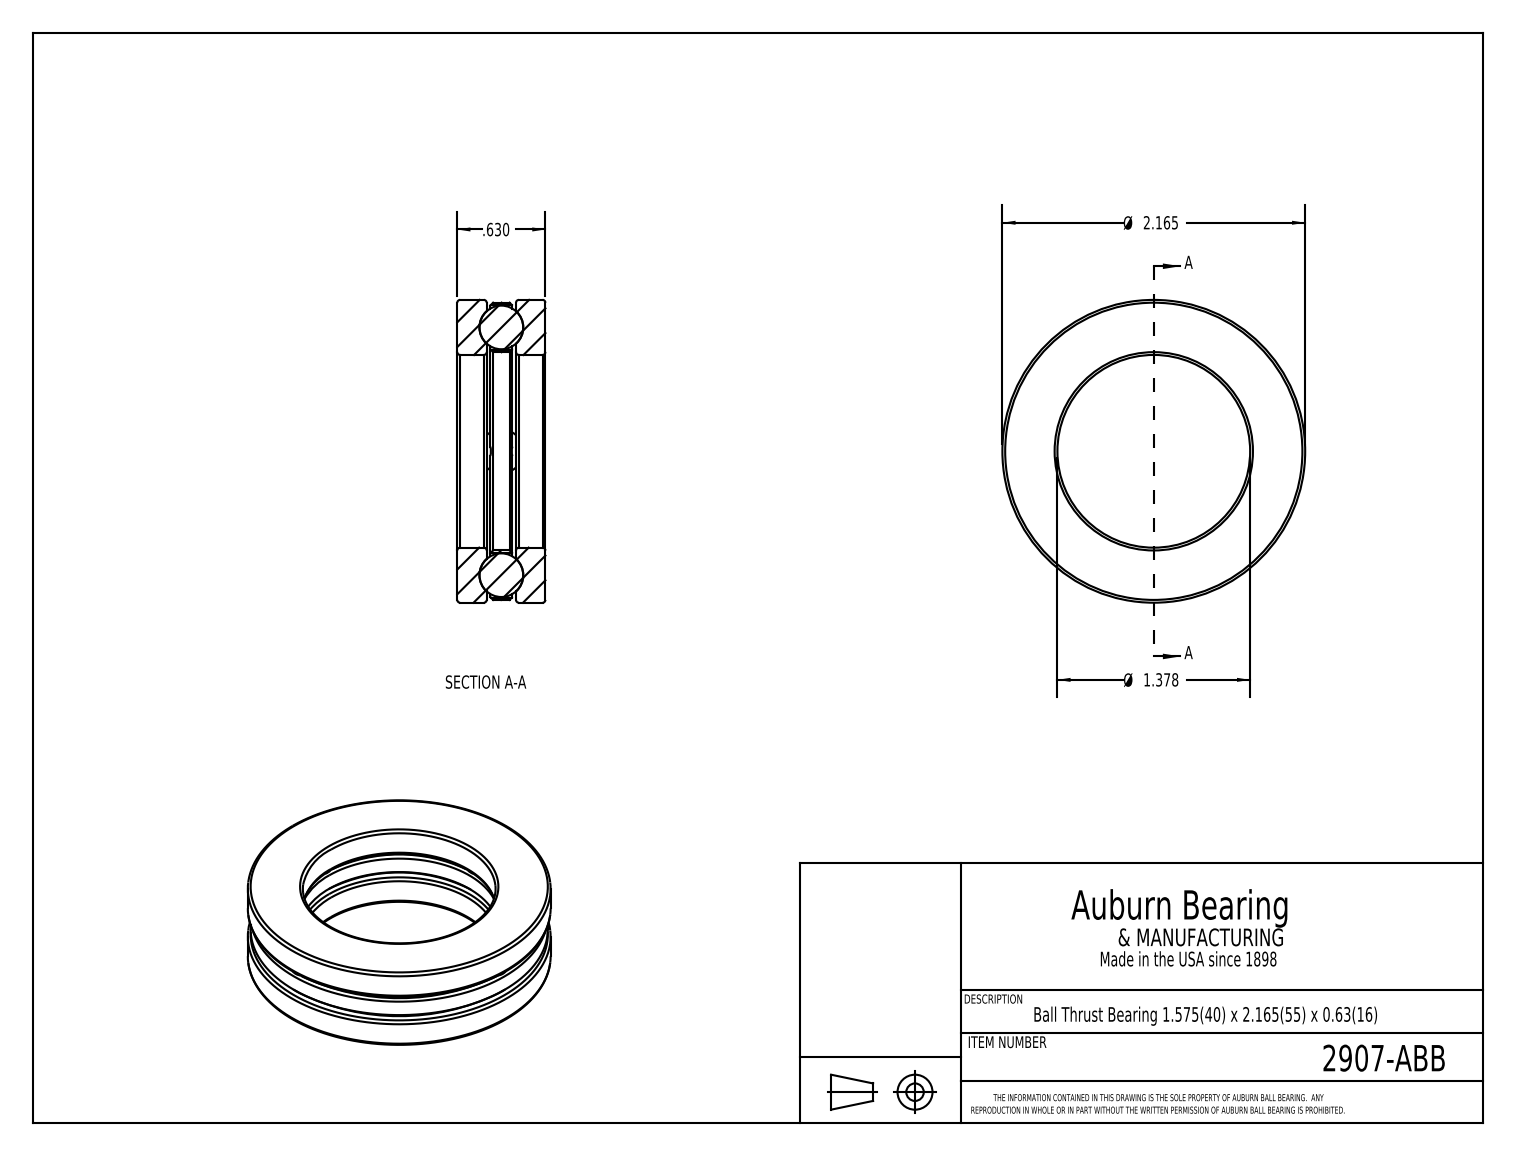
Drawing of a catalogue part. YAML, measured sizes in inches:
part_name: "2907-ABB"
step_written_by: "SolidWorks 2017 (CONFIG_CONTROL_DESIGN)"
units: inches
bodies: {solids: 7, faces: 127, planar: 39, cylindrical: 36, other: 52}
overall_size: [2.182, 2.182, 0.63]
volume: 1.22
surface_area: 22.81
round_holes:
  - {diameter: 0.322, count: 4}
  - {diameter: 0.157, count: 2}
  - {diameter: 0.21, count: 2}
  - {diameter: 1.575, count: 1}
  - {diameter: 1.615, count: 1}
round_bosses_or_shafts:
  - {diameter: 0.63, count: 2}
  - {diameter: 2.165, count: 1}
  - {diameter: 2.125, count: 1}
face_to_face_distances: [0.21, 0.42, 0.63, 0.236, 0.184, 0.394, 1.87, 0.295, 0.315, 2.165]
hole_center_spacings: [0.935, 1.322, 1.87]
